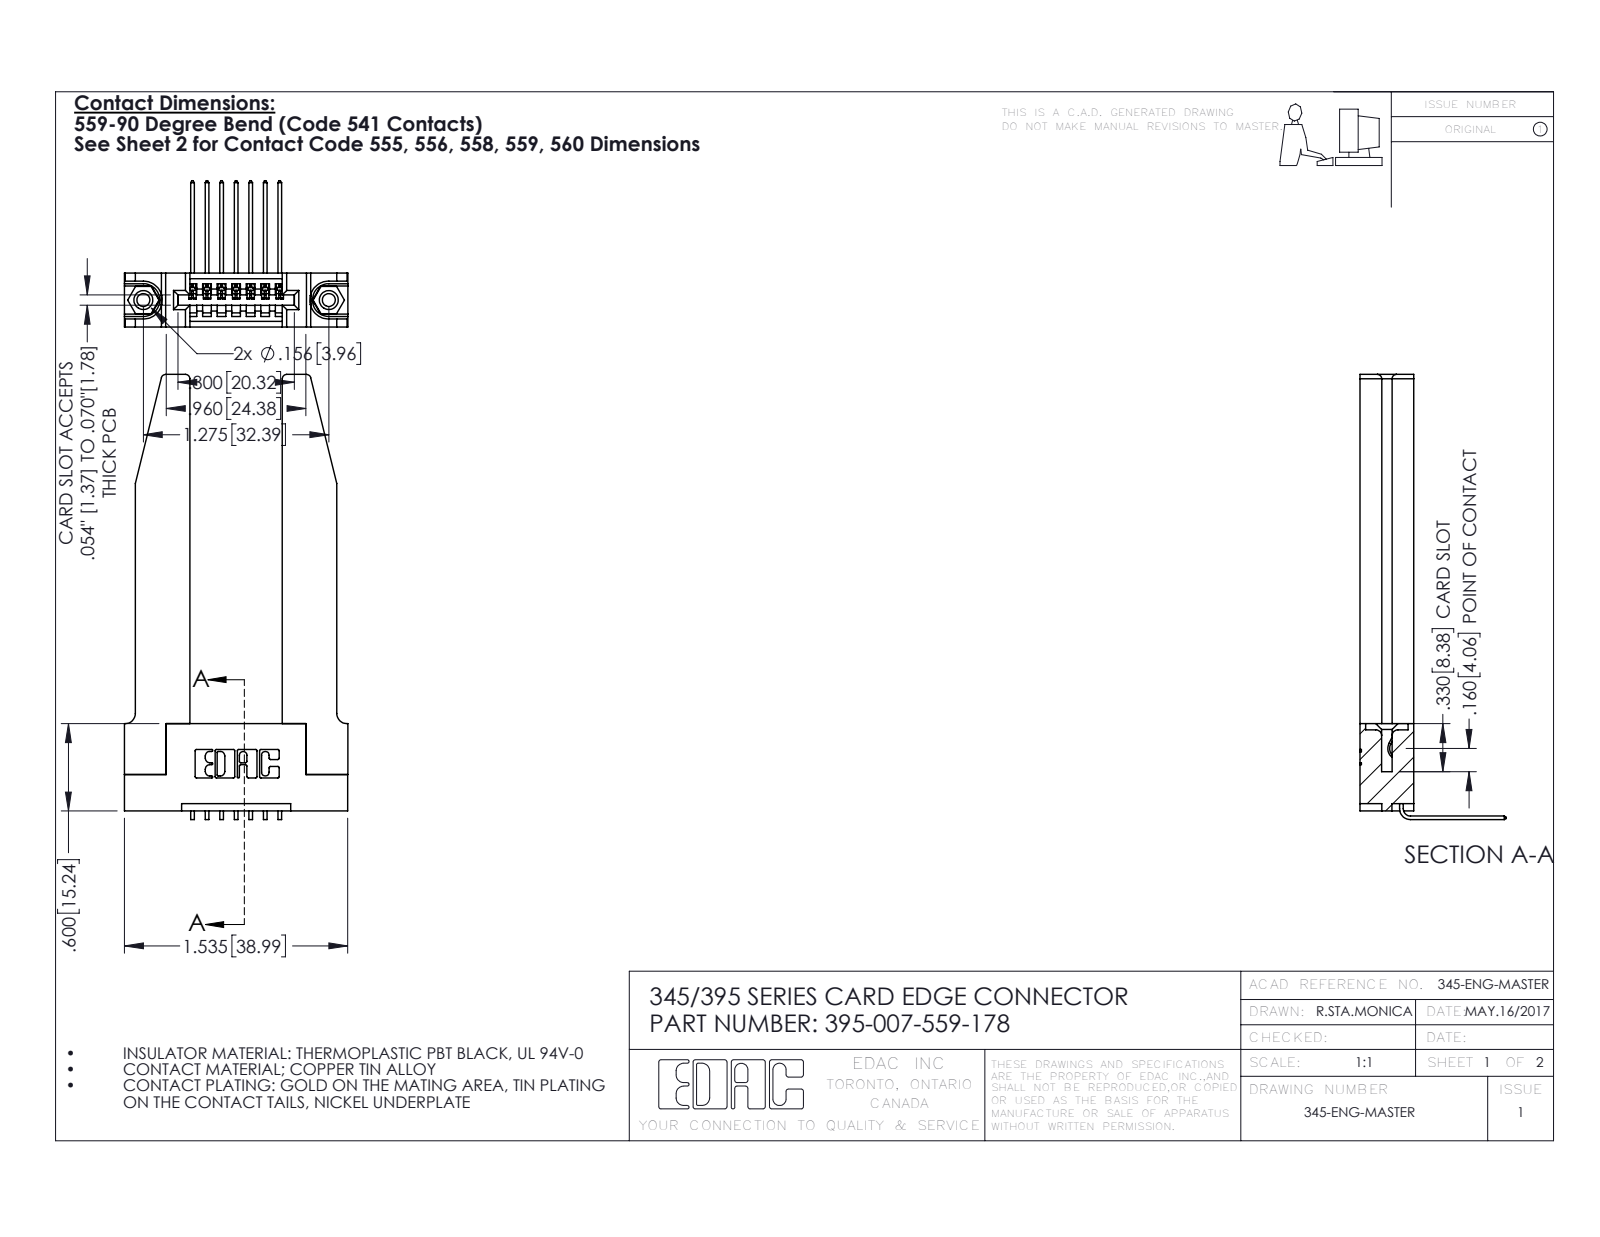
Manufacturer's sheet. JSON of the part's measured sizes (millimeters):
{"part_name": "395-007-559-178; 345-250-001_345-250-001-102; 345-220-078_345-220-078; 345 Part_Flush Mounting Lugs - 0.156 Dia-TH (+1 more)", "step_written_by": "SolidWorks 2016 (CONFIG_CONTROL_DESIGN)", "units": "millimeters", "bodies": {"solids": 12, "faces": 780, "planar": 516, "cylindrical": 212, "other": 52}, "overall_size": [77.7, 39, 25.5], "volume_mm3": 11200, "surface_area_mm2": 11080, "round_holes": [[2.3, 2], [3.2, 2], [4, 2], [1.6, 1]], "round_bosses_or_shafts": [[3.9, 2]], "partial_cylinders_radius": [[0.3, 22], [0.2, 14], [0.8, 8], [0.2, 6], [0.8, 6], [0.7, 3], [0.8, 2], [1, 2]], "face_to_face_distances": [9.4, 3.8, 5.6, 16.1, 1.8, 3.8, 2, 7.6, 5.1, 2.4], "hole_center_spacings": [6.9, 26.5, 32.4]}
